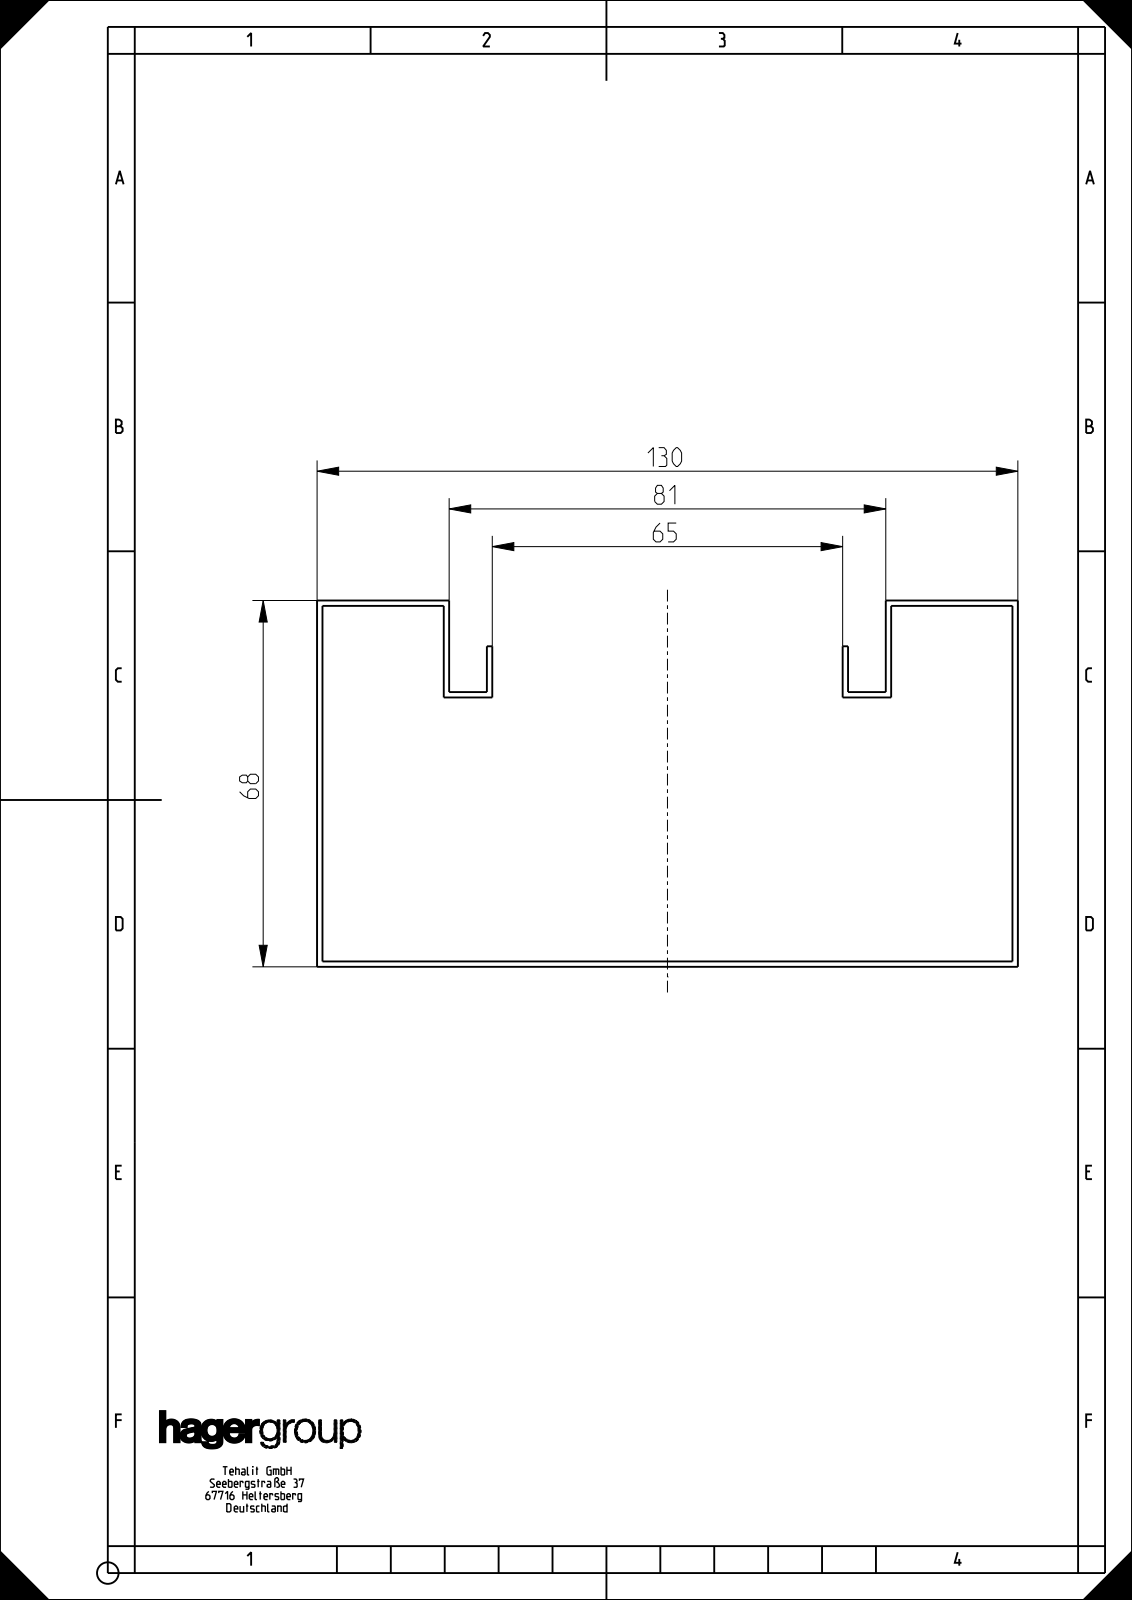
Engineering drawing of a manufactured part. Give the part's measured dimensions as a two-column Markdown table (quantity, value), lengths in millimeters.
| quantity | value |
| --- | --- |
| part name | BRS651301KUN |
| STEP written by | CREO PARAMETRIC BY PTC INC, 2022162 (AUTOMOTIVE_DESIGN) |
| units | millimeters |
| bodies | 1 solid, 858 faces (826 planar, 32 cylindrical, 0 other) |
| overall size | 2000 × 130 × 68 |
| volume | 752 277 mm³ |
| surface area | 1 512 000 mm² |
| round holes (diameter × count) | 6.5 × 16 |
| main face-to-face distances | 1, 129, 67, 23.5, 105.5, 130, 128, 66, 68, 31.5 |
| hole center spacings | 250, 259.62, 500, 504.88, 750, 753.26, 70, 1000 |
